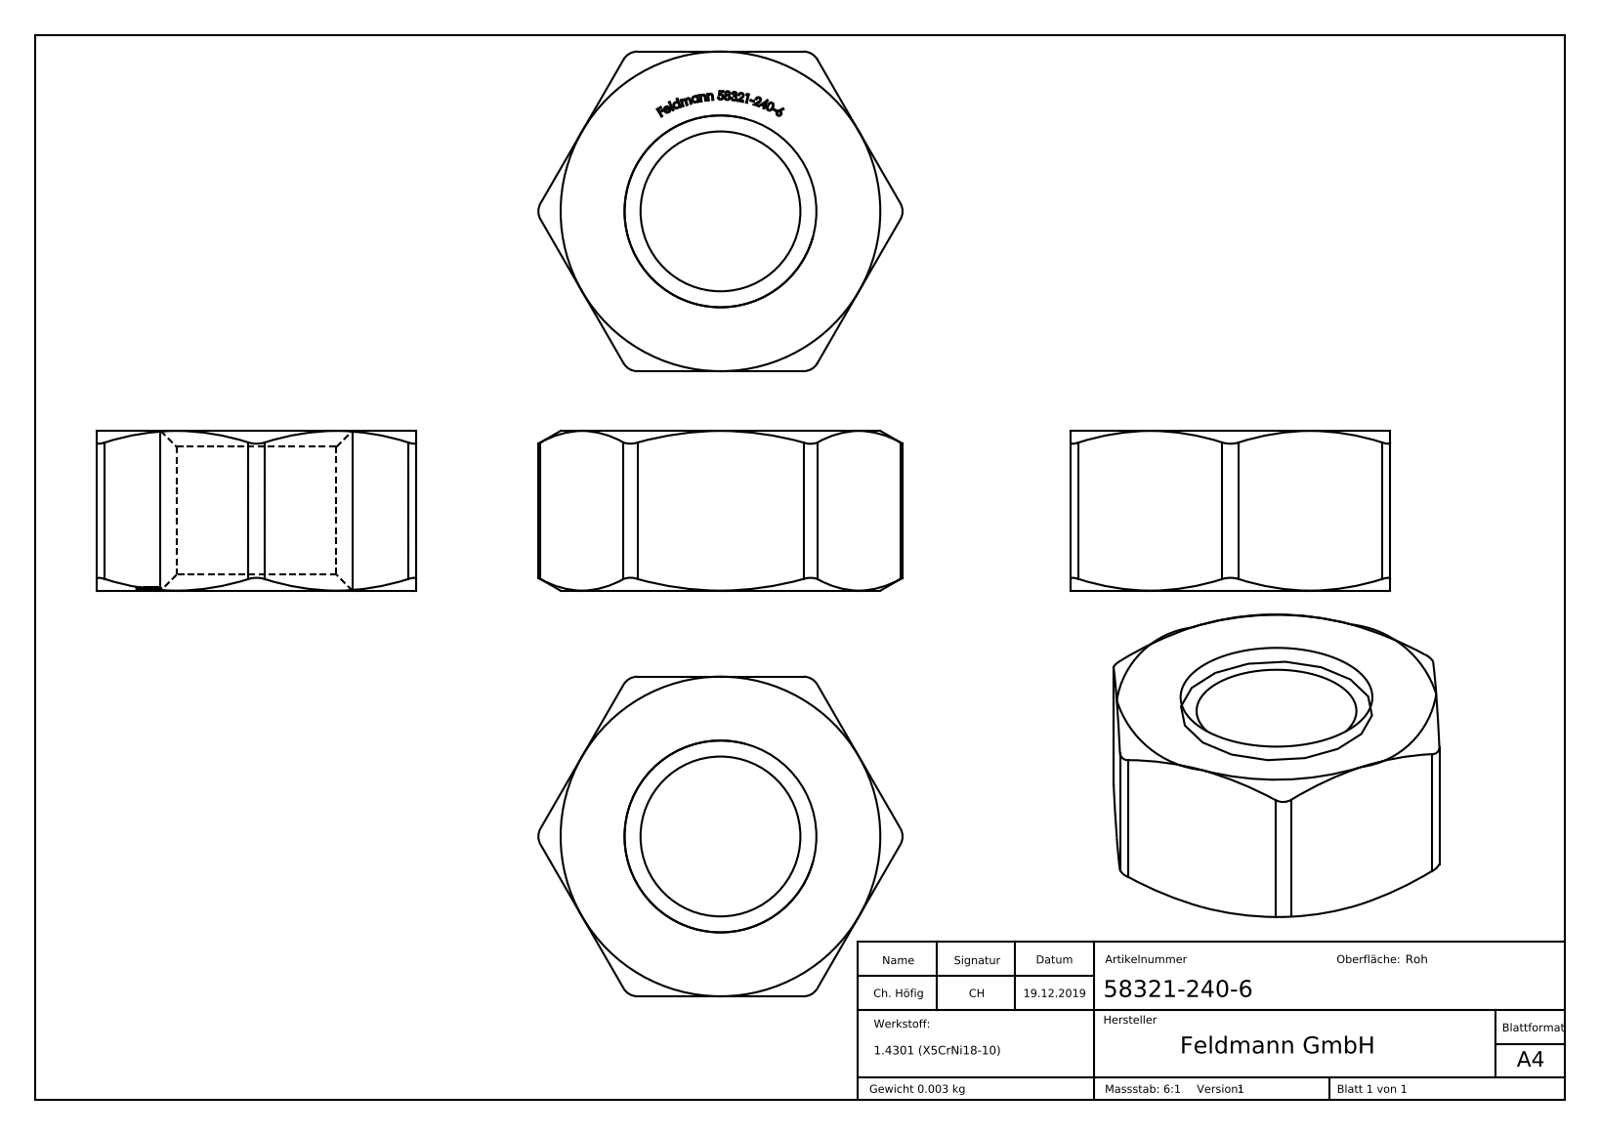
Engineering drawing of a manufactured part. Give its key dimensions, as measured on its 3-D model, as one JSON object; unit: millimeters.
{"part_name": "58321-240-6", "step_written_by": "SolidWorks 2015 (CONFIG_CONTROL_DESIGN)", "units": "millimeters", "bodies": {"solids": 1, "faces": 29, "planar": 8, "cylindrical": 7, "other": 14}, "overall_size": [22, 11.39, 10], "volume_mm3": 328, "surface_area_mm2": 368, "round_holes": [[5, 1]], "partial_cylinders_radius": [[0.5, 6]], "face_to_face_distances": [10, 5]}
